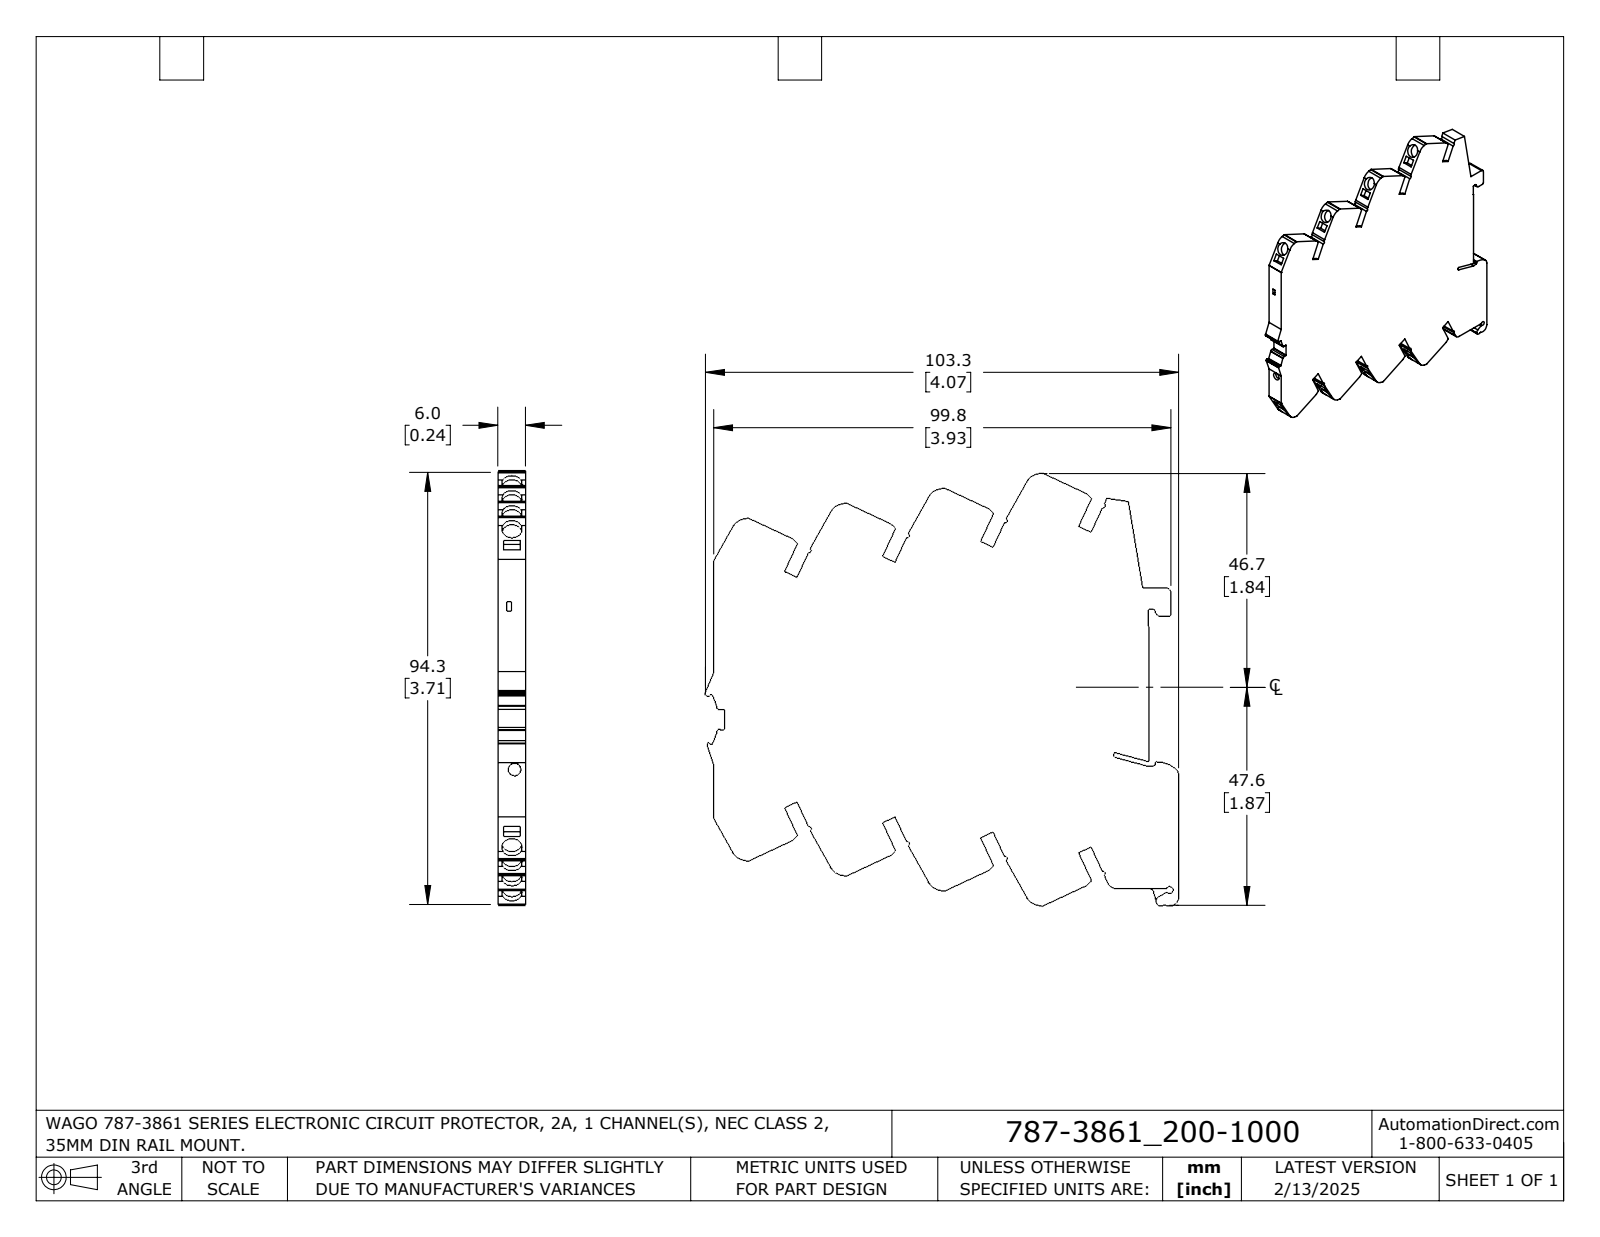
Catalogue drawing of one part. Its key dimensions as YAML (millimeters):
part_name: "787-3861_200-1000_HI"
step_written_by: "SolidWorks 2024 (AUTOMOTIVE_DESIGN)"
units: millimeters
bodies: {solids: 1, faces: 262, planar: 197, cylindrical: 65, other: 0}
overall_size: [103.3, 94.26, 6]
volume: 43992
surface_area: 18864
round_holes:
  - {diameter: 4.4, count: 8}
  - {diameter: 2.7, count: 1}
partial_cylinders:
  - {radius: 0.2, count: 13}
  - {radius: 0.5, count: 12}
  - {radius: 0.4, count: 8}
  - {radius: 3.35, count: 8}
  - {radius: 1, count: 5}
  - {radius: 0.3, count: 3}
  - {radius: 2, count: 3}
  - {radius: 0.45, count: 2}
face_to_face_distances: [6, 17.99, 17.02, 12.01, 3, 35.98, 12, 24.01, 14.99, 34.04]
hole_center_spacings: [13.35, 13.34, 26.7, 26.71, 40.05]
